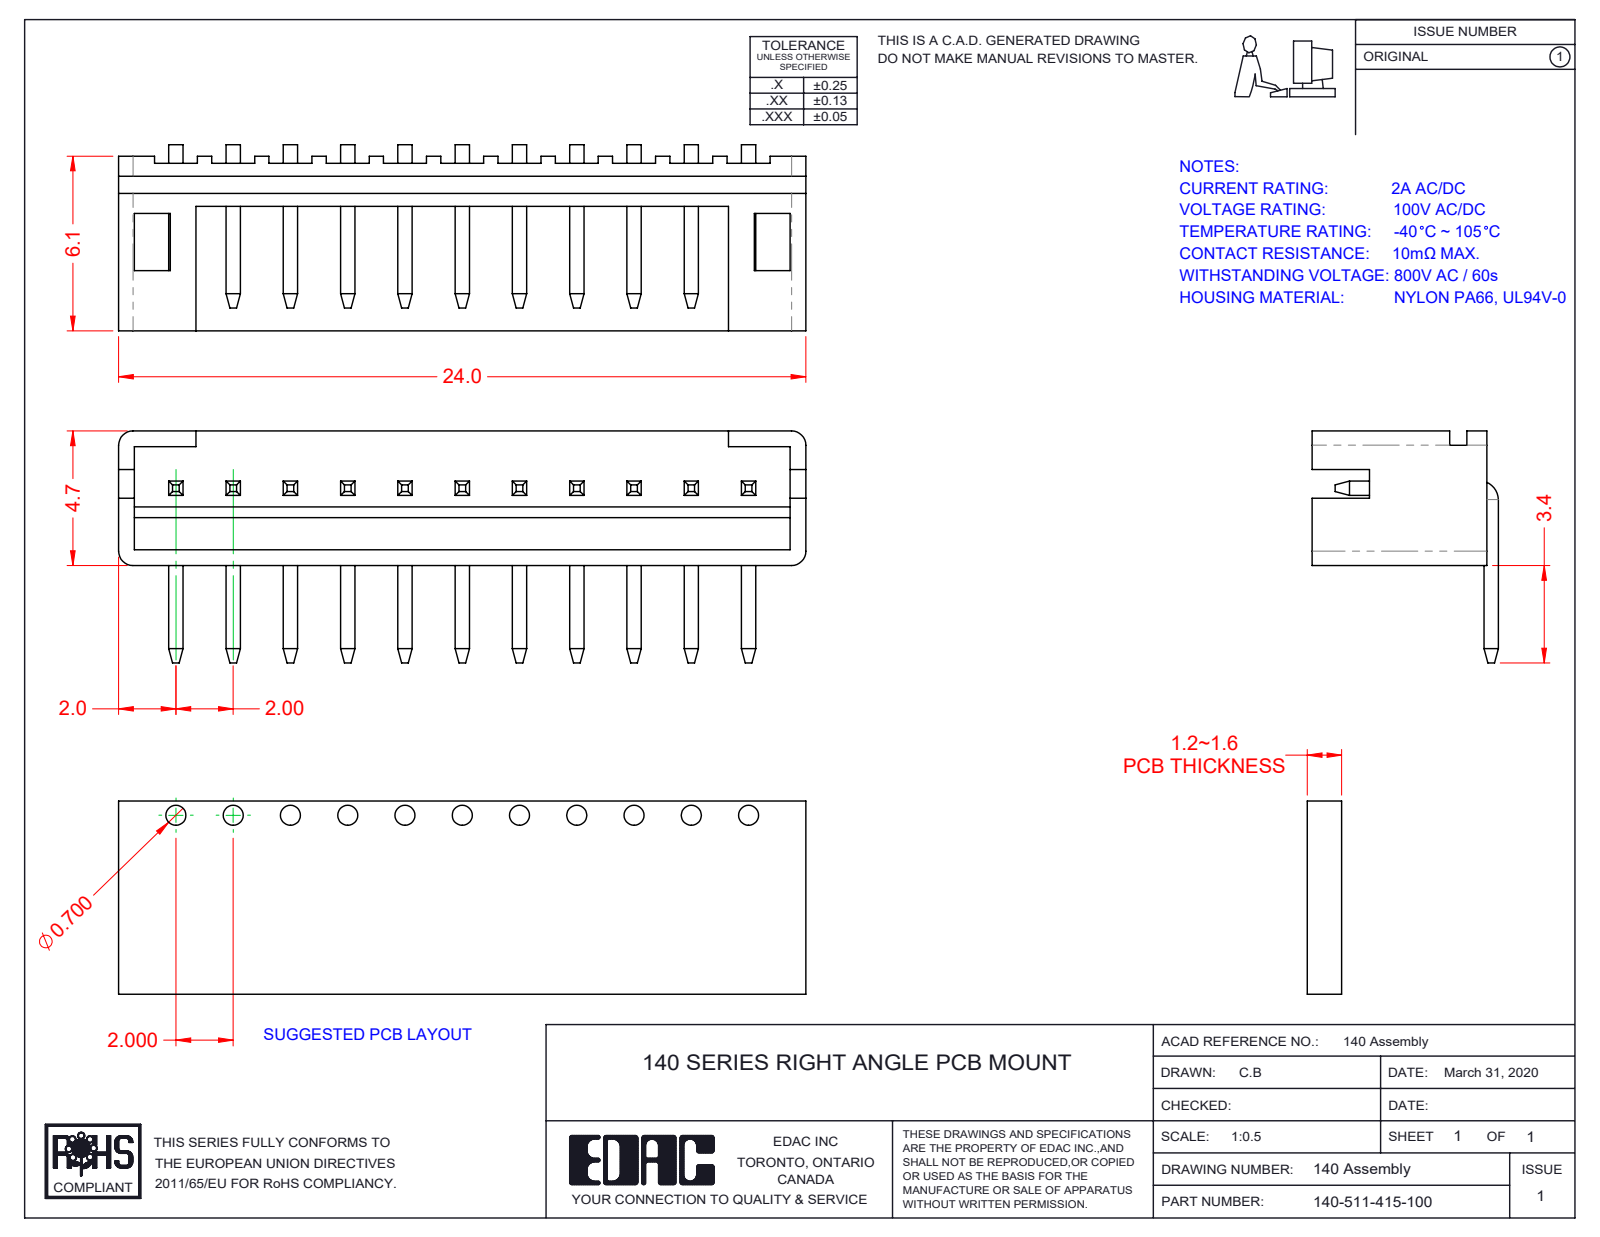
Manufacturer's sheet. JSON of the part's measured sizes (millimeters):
{"part_name": "RA LI Contact_Str; RA LI Housing_511; 140-511-415-100", "step_written_by": "SolidWorks 2020 (CONFIG_CONTROL_DESIGN)", "units": "millimeters", "bodies": {"solids": 12, "faces": 370, "planar": 342, "cylindrical": 28, "other": 0}, "overall_size": [24, 8.1, 6.5], "volume_mm3": 259, "surface_area_mm2": 977, "partial_cylinders_radius": [[0.5, 4], [0.15, 1], [0.65, 1]], "face_to_face_distances": [0.55, 0.5, 1.5, 1.75, 2, 6, 4, 0.65, 4.15, 6.5]}
